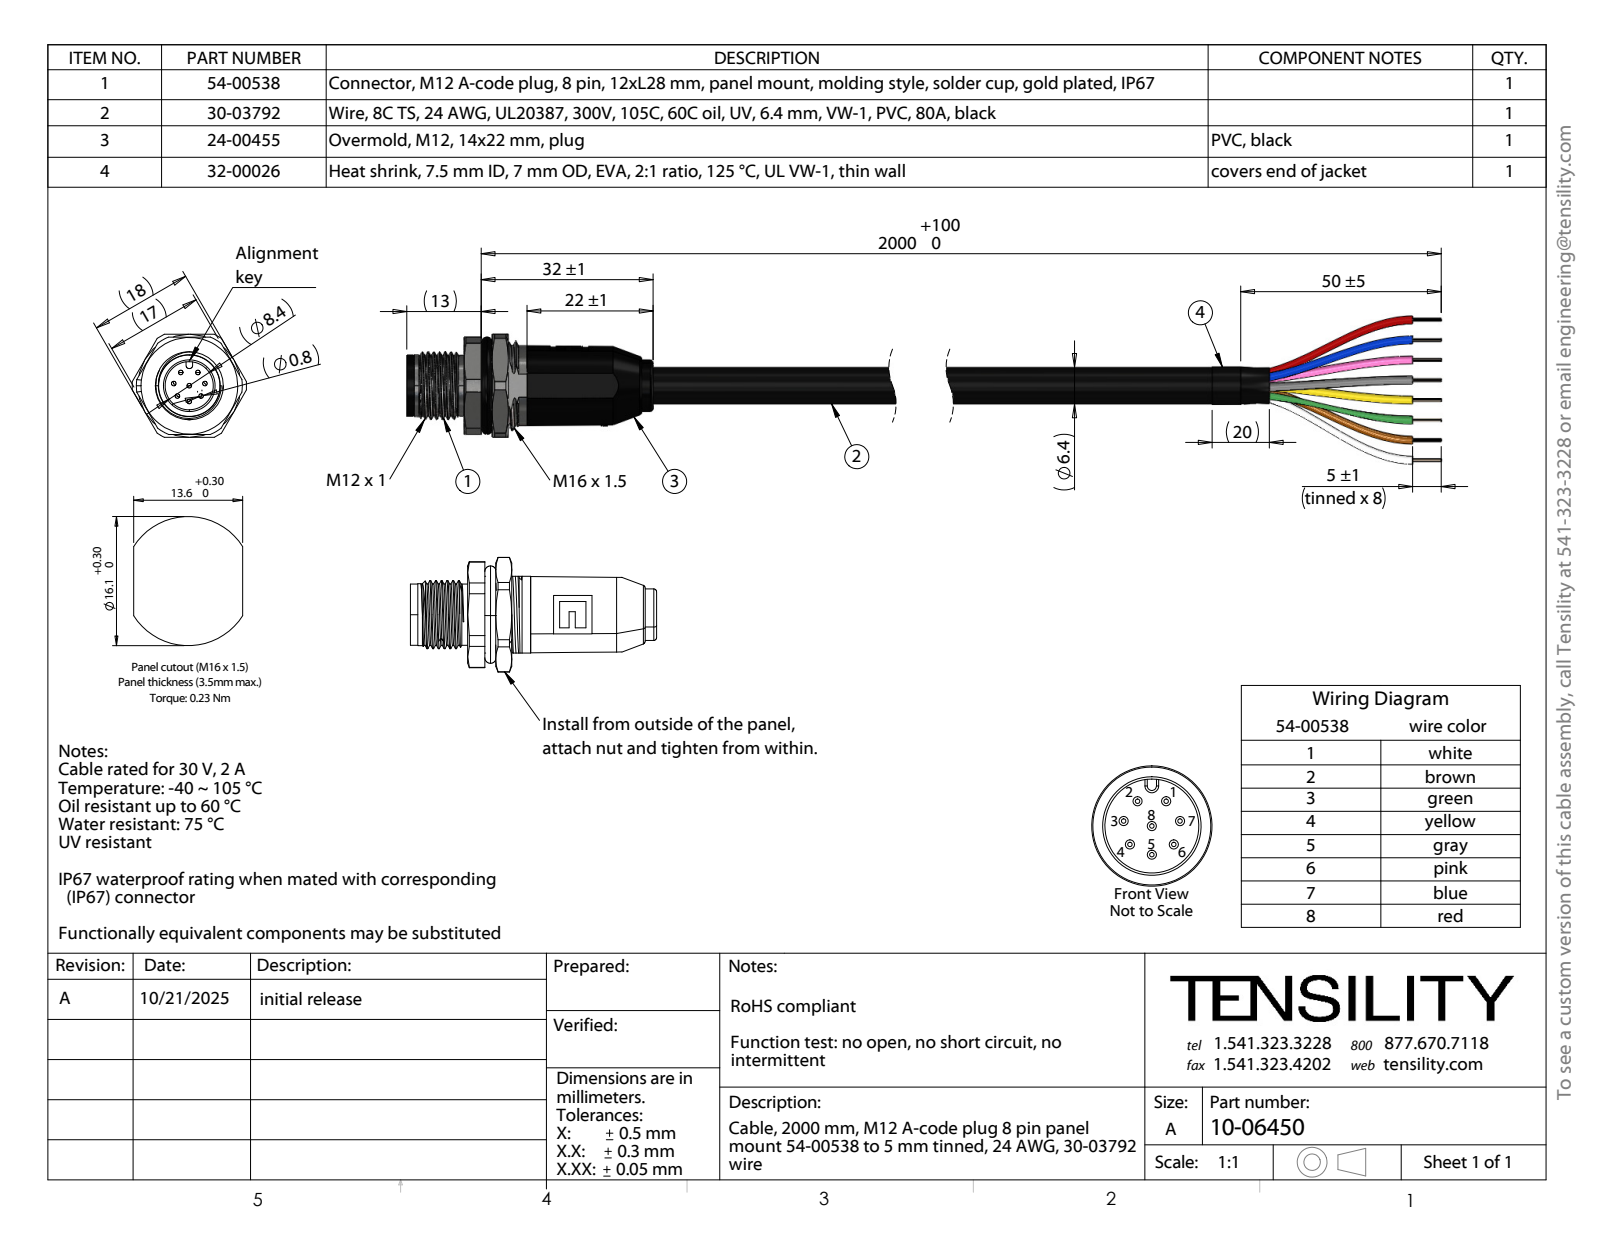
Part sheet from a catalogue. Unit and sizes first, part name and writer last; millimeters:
Units: millimetres
Overall size (bounding box): 228 × 25.9 × 20
Round holes (diameter × count): ⌀0.96 ×8, ⌀7.5 ×1, ⌀8.4 ×1, ⌀9.4 ×1, ⌀9.6 ×1, ⌀12.2 ×1, ⌀14.7 ×1
Round bosses / shafts (diameter × count): ⌀1.5 ×8, ⌀1.4 ×8, ⌀0.8 ×8, ⌀13.94 ×1, ⌀12.5 ×1, ⌀11.86 ×1, ⌀11 ×1, ⌀10.8 ×1
Partial cylindrical surfaces — rounded edges, fillets, slot ends (radius × count): R0.5 ×2, R2.75 ×1, R7.04 ×1, R7.9 ×1, R9.25 ×1, R10 ×1
Main face-to-face distances: 5.5, 11, 0.5, 9.5, 4, 8, 1.5, 17.5, 18, 5.3
Hole centre spacings: 2.75, 4.15, 2.27, 2.28, 2.29, 4.64, 5.27, 5.28
Volume: 10 741 mm³ · Surface area: 11 228 mm²
Bodies: 327 solids, 1810 faces (779 planar, 838 cylindrical, 193 other)
Part name (STEP PRODUCT): 24-00455; 54-00538; 10-06450; 56-00046 (+2 more)
STEP written by: SolidWorks 2025 (CONFIG_CONTROL_DESIGN)
